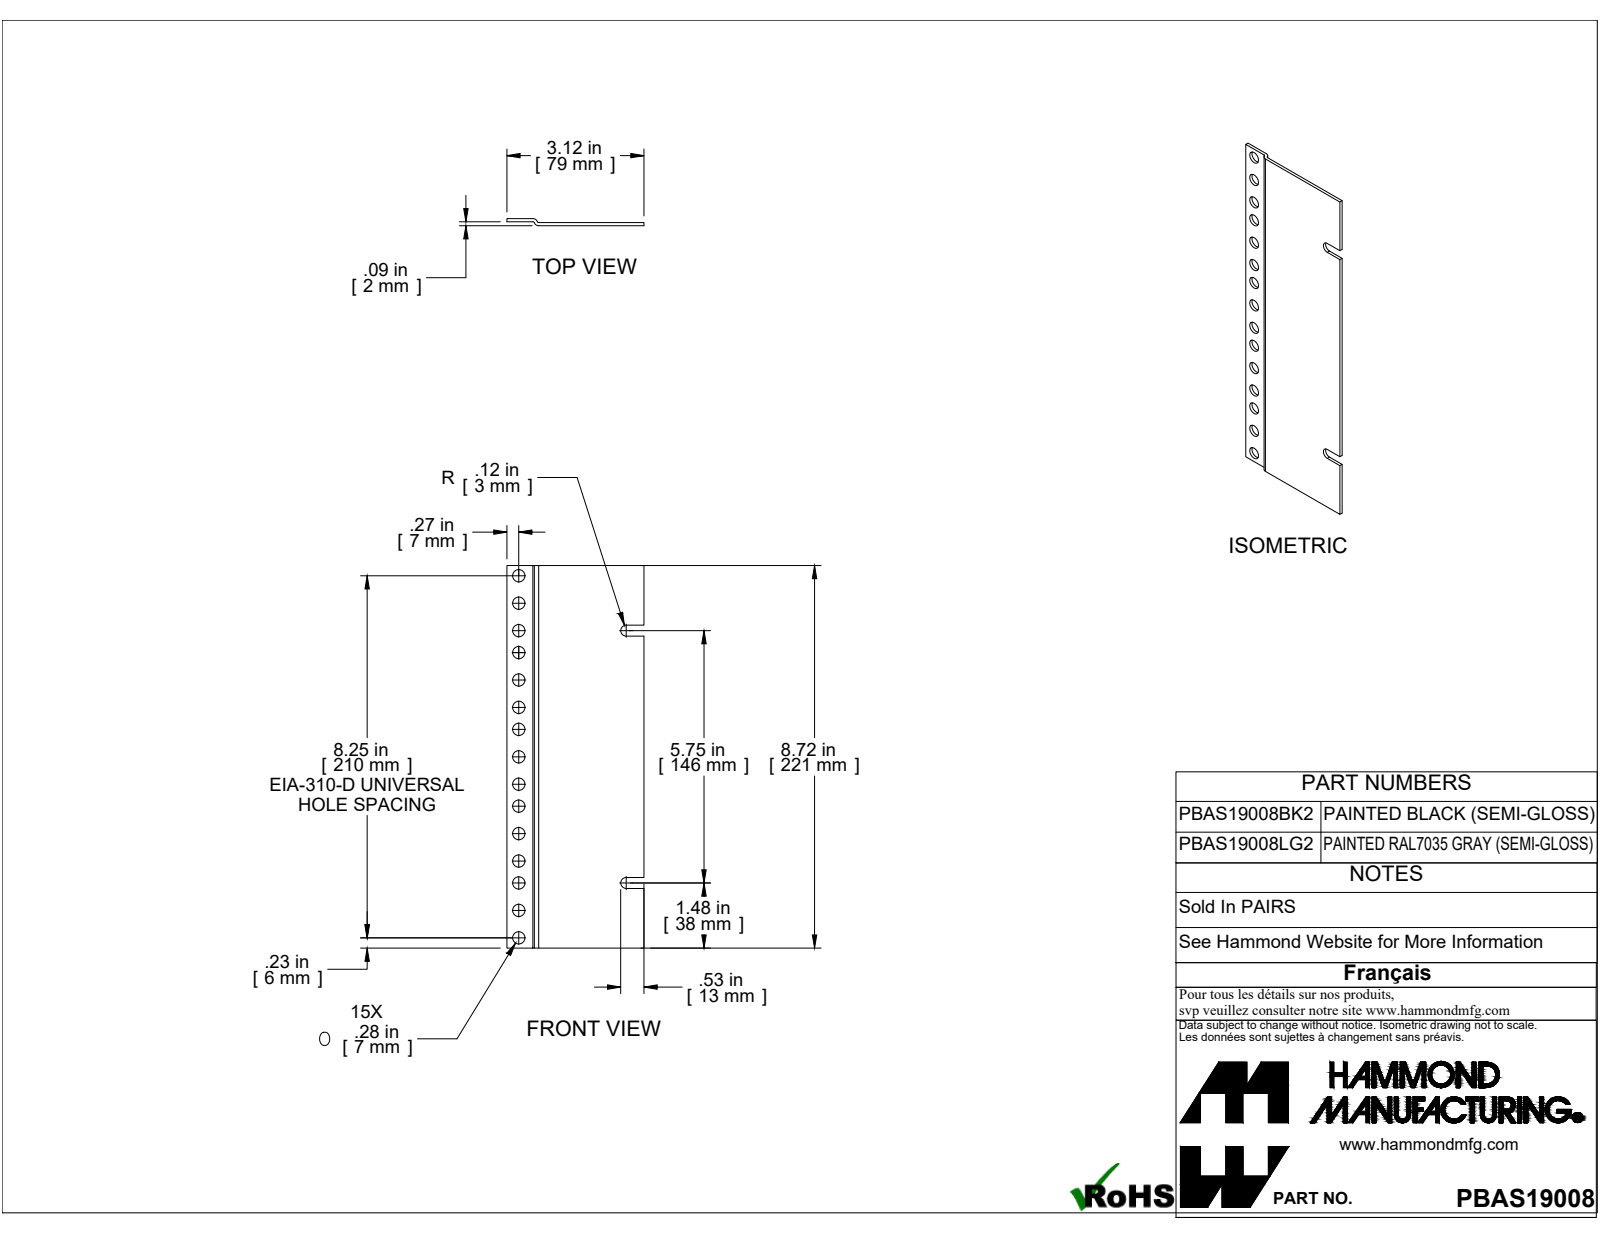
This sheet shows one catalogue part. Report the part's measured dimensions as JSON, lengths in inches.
{"part_name": "PBAS19008LG2", "step_written_by": "SolidWorks 2019 (CONFIG_CONTROL_DESIGN)", "units": "inches", "bodies": {"solids": 1, "faces": 35, "planar": 14, "cylindrical": 21, "other": 0}, "overall_size": [8.718, 3.125, 0.162], "volume_in3": 1.9, "surface_area_in2": 55.58, "round_holes": [[0.281, 15]], "partial_cylinders_radius": [[0.036, 2], [0.108, 2], [0.125, 2]], "face_to_face_distances": [0.072, 0.09, 0.162, 0.018, 0.09, 0.072, 3.125, 8.718, 1.359, 7.359], "hole_center_spacings": [1.75, 0.625, 1.125, 2.875, 3.5, 0.625, 1.25, 2.375]}
